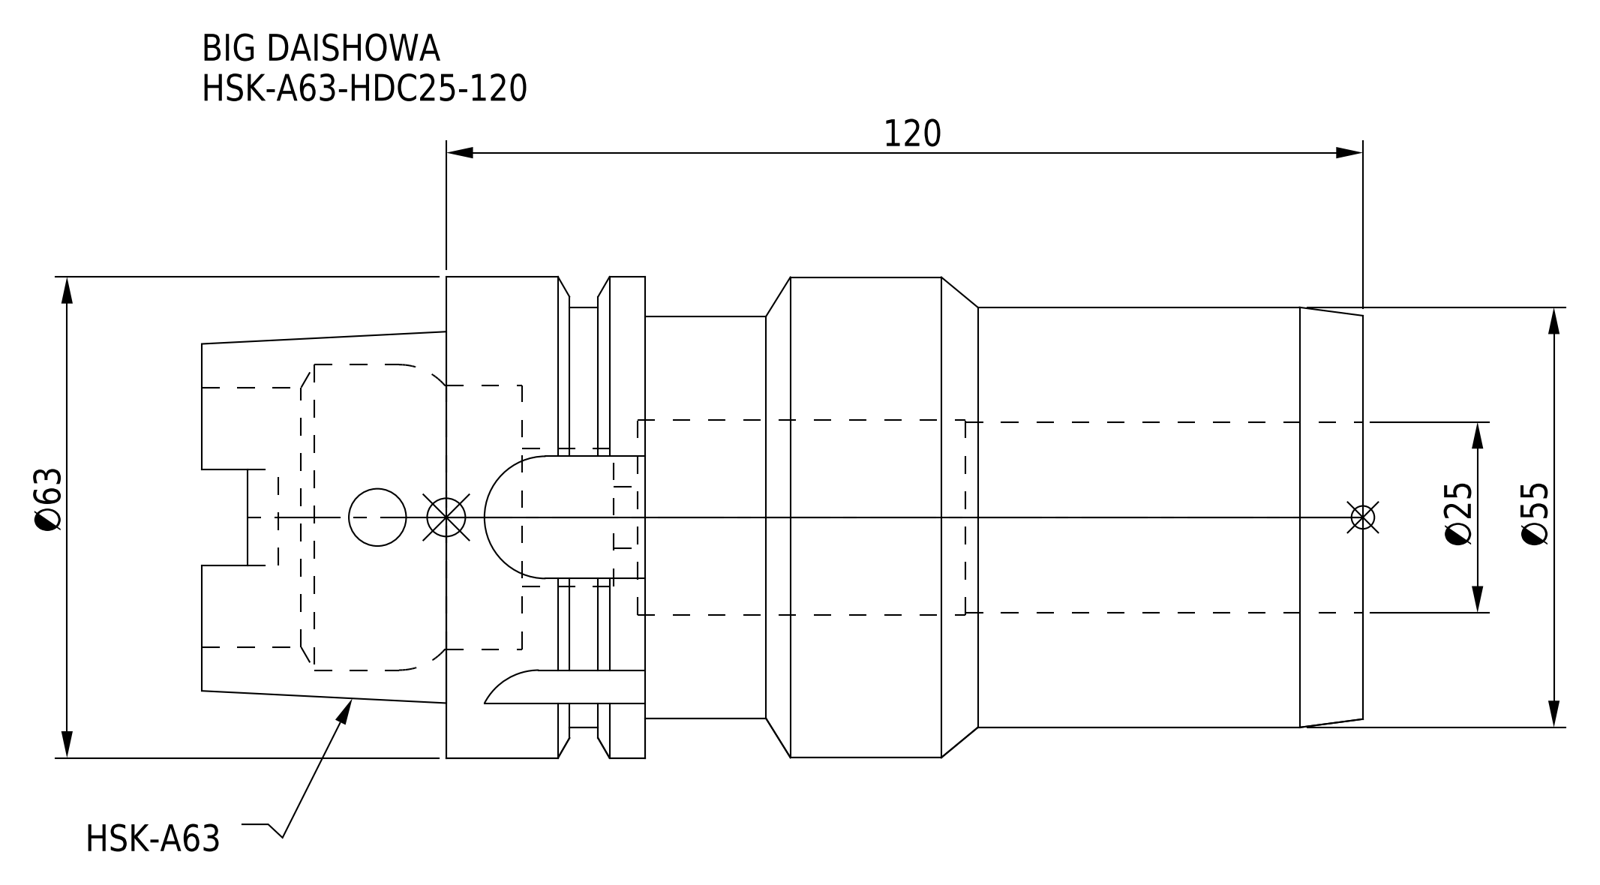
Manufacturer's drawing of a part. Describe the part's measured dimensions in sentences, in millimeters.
The part is named "HSK-A63-HDC25-120". Its 3-D file was written by "CREO PARAMETRIC BY PTC INC, 2016380 (AUTOMOTIVE_DESIGN)". It is 1 solid with 99 faces: 38 planar, 41 cylindrical and 20 other. Overall it measures 152 by 63 by 63 millimeters. Its volume is 270 492 cubic millimeters and its surface area 47 345 square millimeters. Round holes: 1 of diameter 7.5, 1 of diameter 8, 1 of diameter 18, 1 of diameter 25, 1 of diameter 25.5, 1 of diameter 34, 1 of diameter 34.5, 1 of diameter 40. Round bosses or shafts: 1 of diameter 63, 1 of diameter 62.9, 1 of diameter 55, 1 of diameter 52.6. Partial cylindrical surfaces (rounded edges, fillets, slot ends): 4 of radius 2.88, 4 of radius 8. The main face-to-face distances are 120, 26, 94, 110.05, 16.05, 9.95, 1, 95, 15.05, 25.
